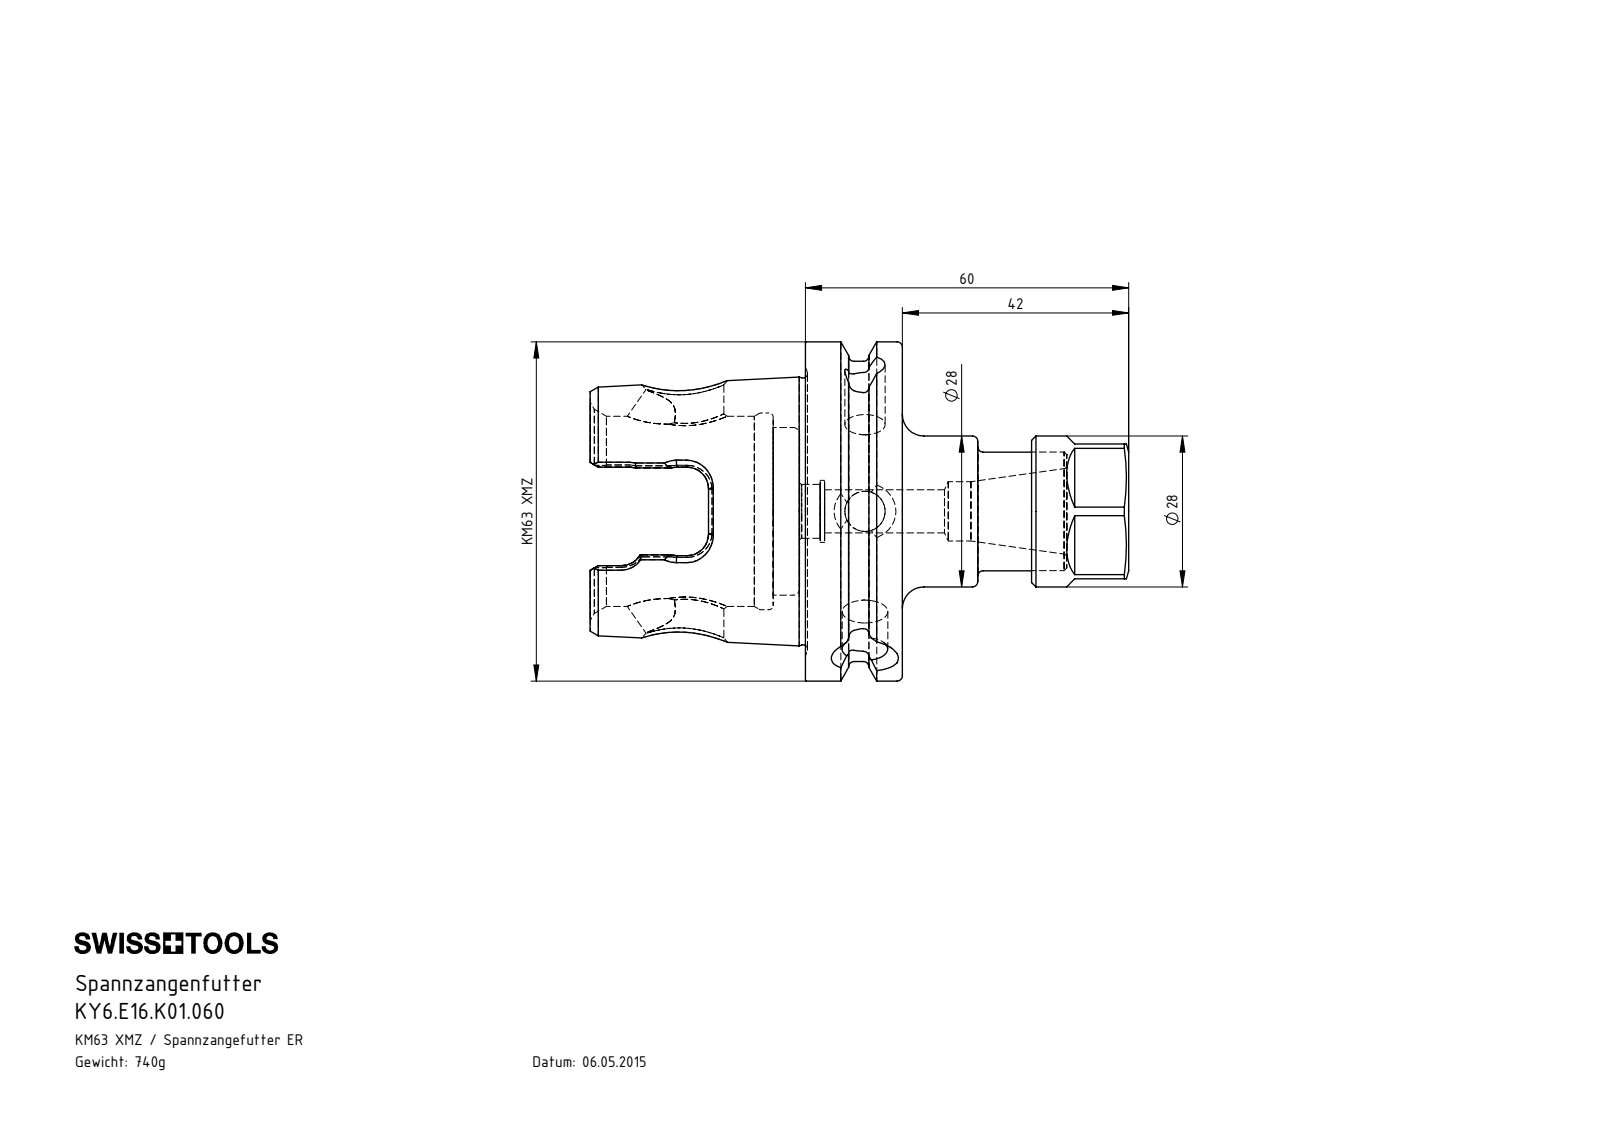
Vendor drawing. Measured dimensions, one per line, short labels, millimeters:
name: KY6-E16.K01.060_B; E16-ER2.001.018; KY6.E16.K01.060
written by: SolidWorks 2017 (CONFIG_CONTROL_DESIGN)
unit: mm
bodies: 2 solids, 270 faces (67 planar, 64 cylindrical, 139 other)
size: 99.95 × 62.95 × 62.95
volume: 94 257 mm³; area: 26 616 mm²
holes: 2× ⌀7.47, 1× ⌀8, 1× ⌀8.48, 1× ⌀10, 1× ⌀11, 1× ⌀11.5, 1× ⌀14.5, 1× ⌀15.9, 1× ⌀20.5, 1× ⌀22.5, 1× ⌀31.1, 1× ⌀35.27
bosses: 1× ⌀62.95, 1× ⌀55.7, 1× ⌀28, 1× ⌀22
rounds: 6× R4, 2× R7.04, 2× R9.6
face distances: 18, 1.1, 19.1, 24, 25, 42, 43.1, 60, 4.9, 6
